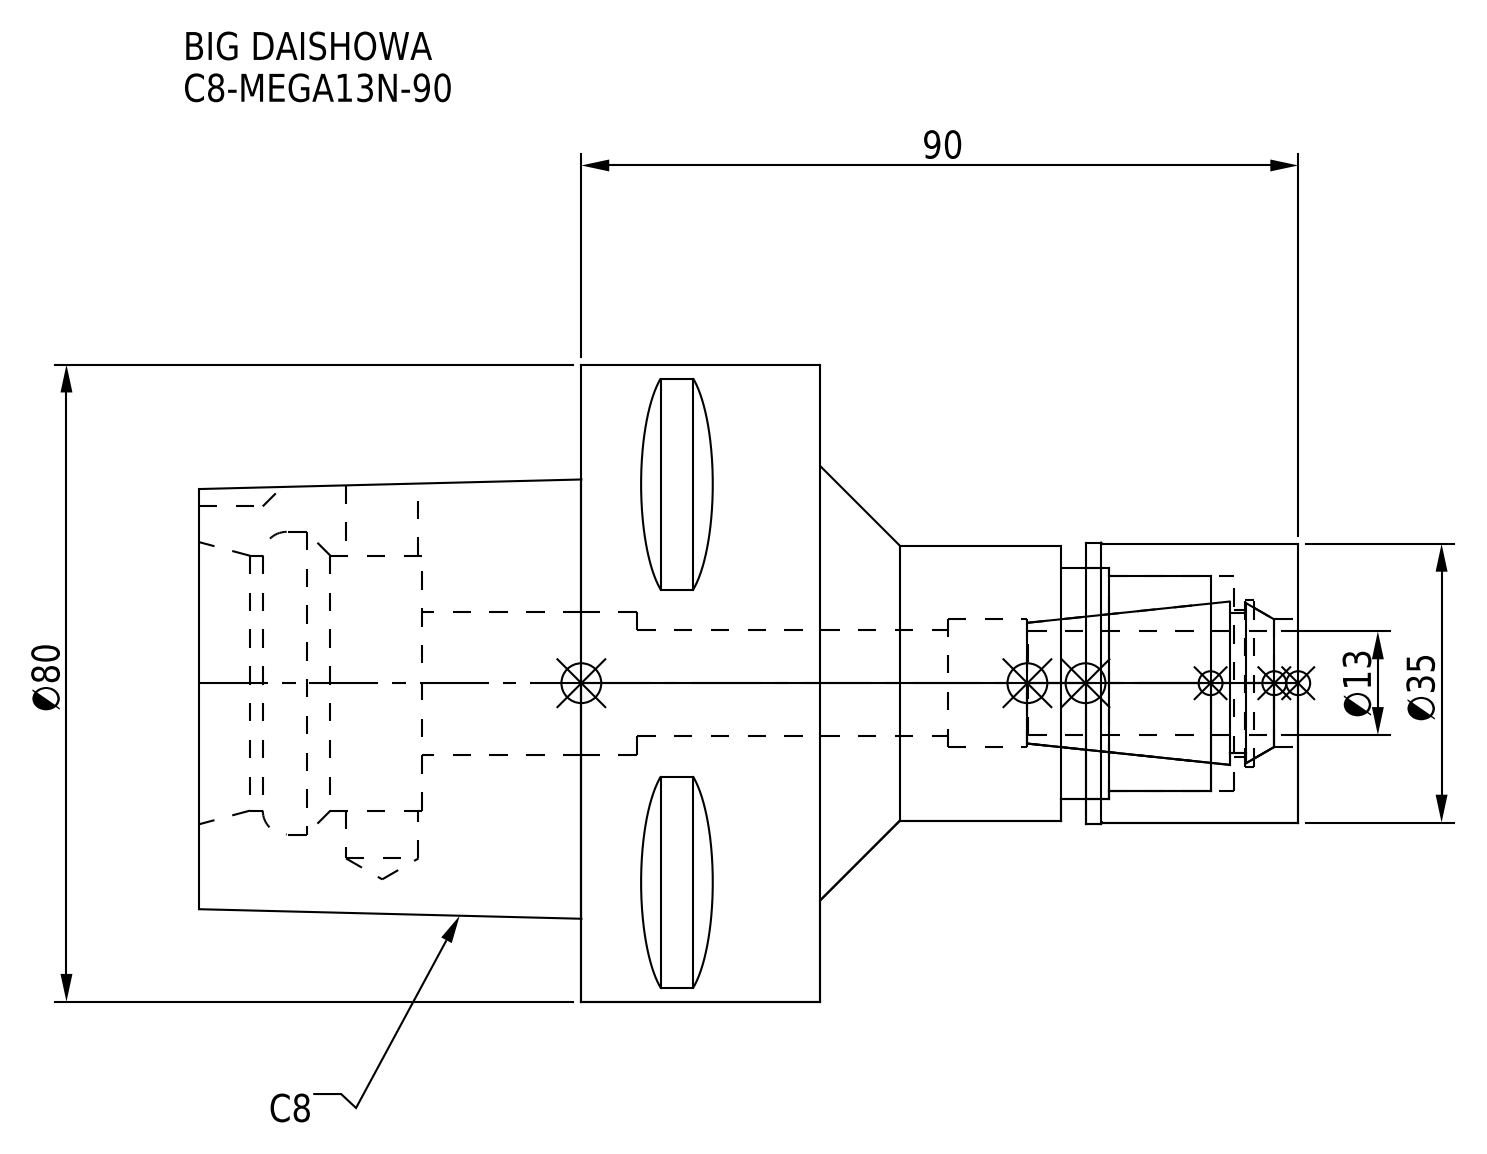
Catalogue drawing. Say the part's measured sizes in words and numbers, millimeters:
The part is named "C8-MEGA13N-90-130-FreeParts; C8-MEGA13N-90; C8-MEGA13N-90-130_ASM.stp; DXF_TEMP_ASSY_ASM_4_ASM.stp (+3 more)". Its 3-D file was written by "SolidWorks 2019 (CONFIG_CONTROL_DESIGN)". It is 2 solids with 95 faces: 38 planar, 39 cylindrical and 18 other. Overall it measures 138 by 80 by 80 millimeters. Its volume is 268 900 cubic millimeters and its surface area 45 100 square millimeters. Round holes: 1 of diameter 9.1, 1 of diameter 13.3, 1 of diameter 16, 1 of diameter 18, 1 of diameter 18.5, 1 of diameter 21, 1 of diameter 27, 1 of diameter 29, 1 of diameter 32, 1 of diameter 38. Round bosses or shafts: 1 of diameter 80, 1 of diameter 35.3, 1 of diameter 35, 1 of diameter 34.5. Partial cylindrical surfaces (rounded edges, fillets, slot ends): 1 of radius 6. The main face-to-face distances are 30, 78, 48, 60, 90, 138, 20, 110, 50, 28.
